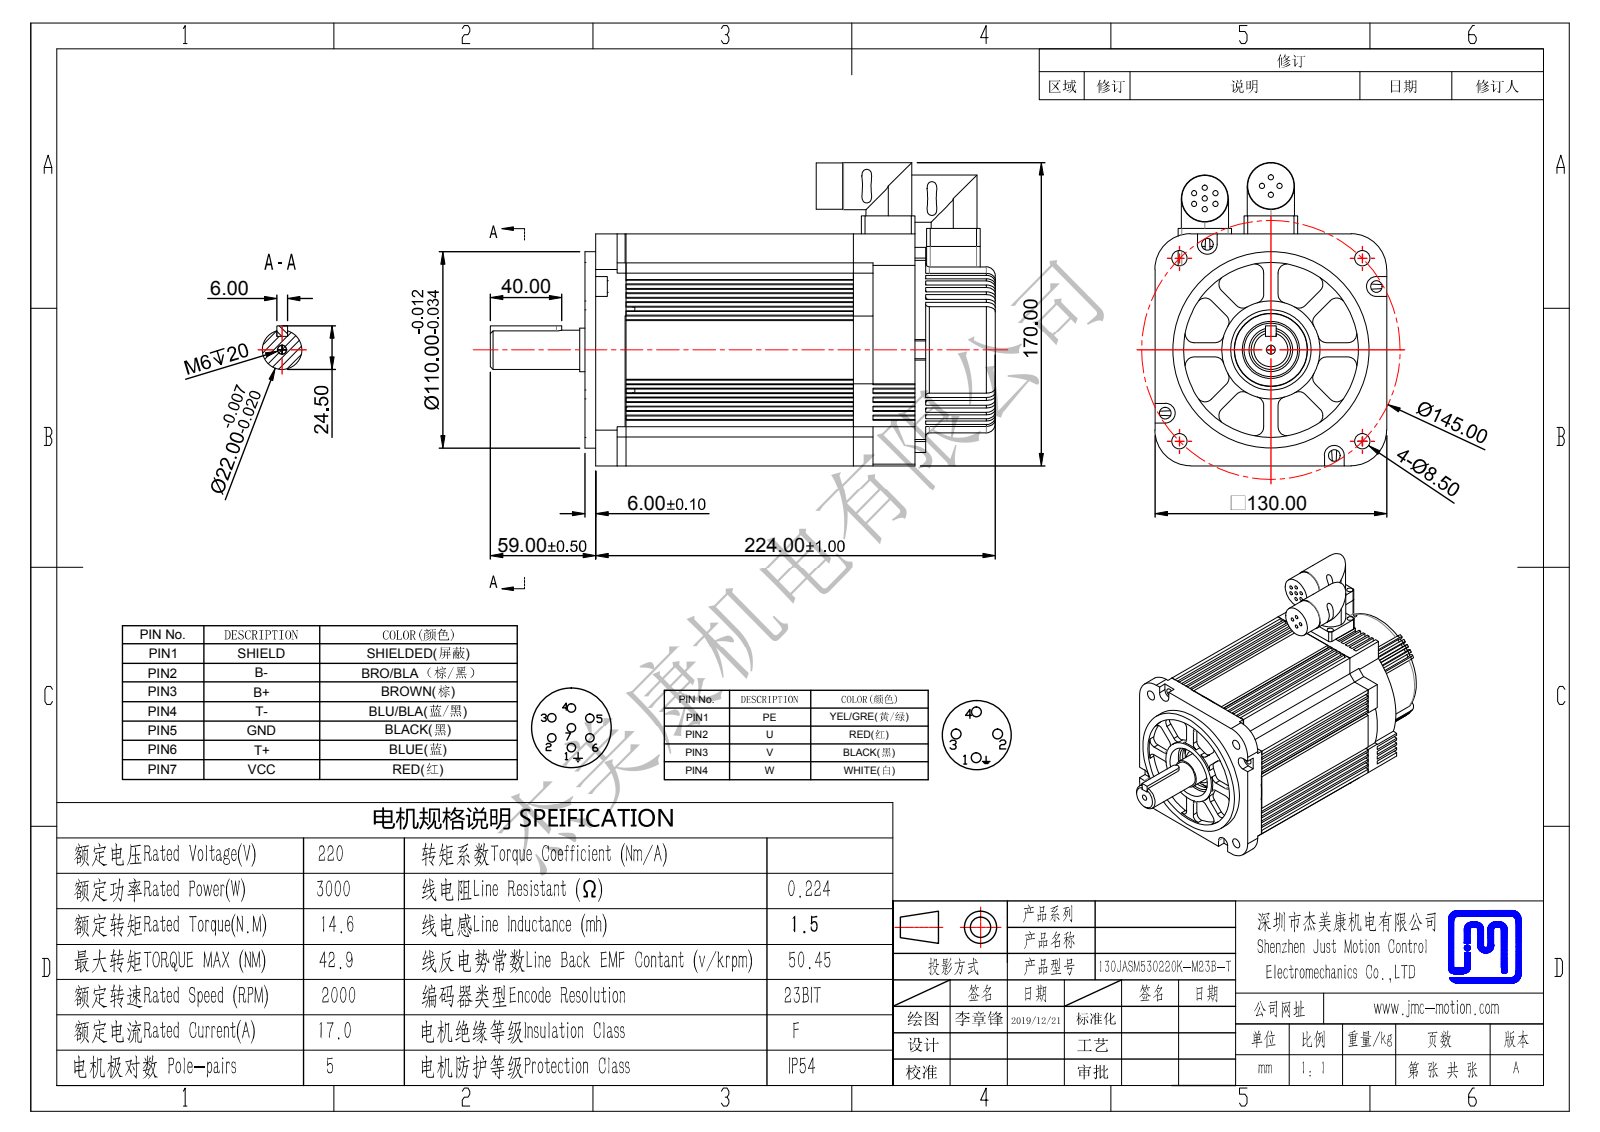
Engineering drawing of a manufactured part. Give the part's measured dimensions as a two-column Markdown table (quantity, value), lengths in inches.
| quantity | value |
| --- | --- |
| part name | 130JASM523215K-M23B-T |
| STEP written by | SolidWorks 2015 (CONFIG_CONTROL_DESIGN) |
| units | inches |
| bodies | 0 solids, 709 faces (364 planar, 260 cylindrical, 85 other) |
| overall size | 11.142 × 6.693 × 5.118 |
| round holes (diameter × count) | 0.118 × 11, 0.213 × 8, 2.165 × 1, 3.661 × 1, 3.976 × 1, 4.331 × 1 |
| round bosses / shafts (diameter × count) | 0.335 × 4, 0.256 × 4, 0.177 × 4, 1.043 × 2, 1.024 × 2, 3.858 × 1, 2.021 × 1, 1.772 × 1 |
| partial cylindrical surfaces (radius × count) | 0.197 × 36, 0.079 × 10, 0.039 × 7, 0.118 × 6, 0.522 × 6, 0.217 × 4, 0.787 × 4, 2.52 × 1 |
| main face-to-face distances | 0.866, 4.252, 5.118, 3.386, 7.047, 8.819, 1.772, 2.913, 2.448, 3.091 |
| hole center spacings | 0.264, 0.945, 0.236, 0.272, 0.426, 1.336, 2.046, 0.472 |
